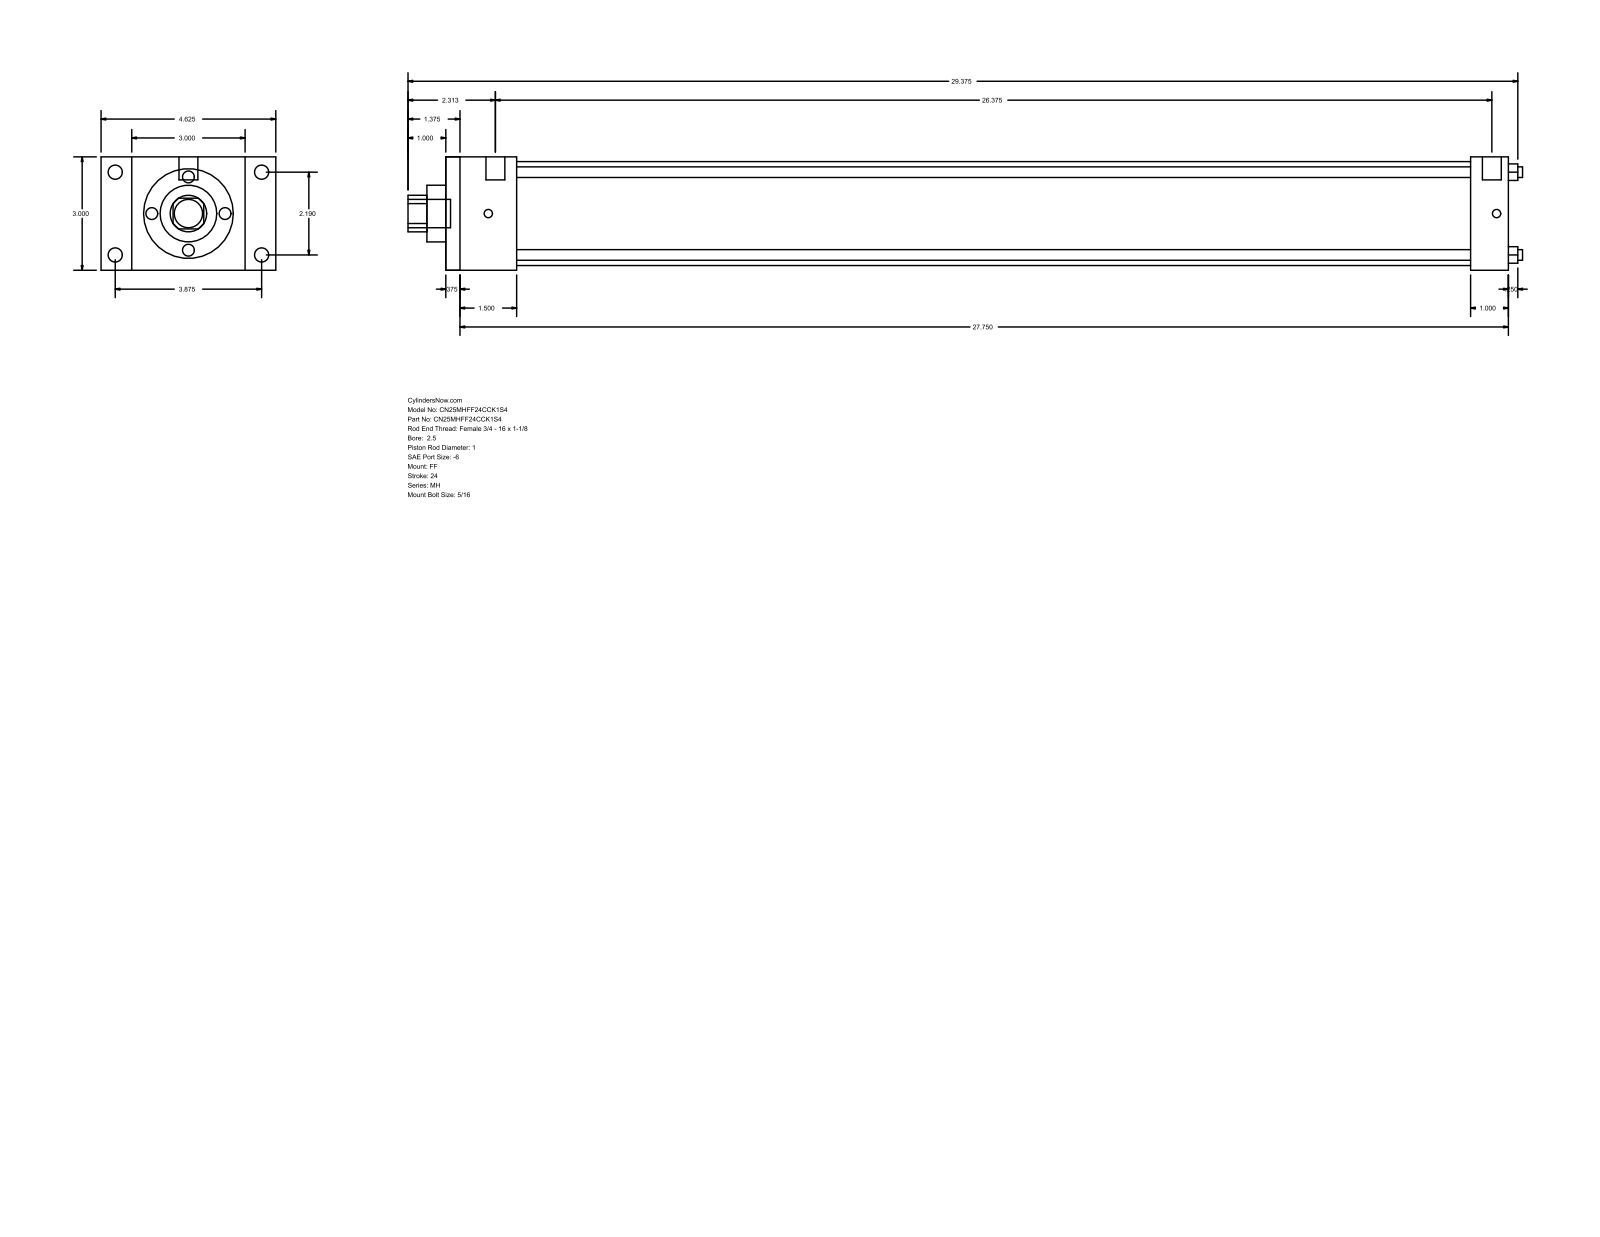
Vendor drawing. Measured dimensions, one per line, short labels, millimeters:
name: MH_FF__0250_1
written by: GSSL Pune (CONFIG_CONTROL_DESIGN)
unit: mm
bodies: 0 solids, 92 faces (64 planar, 28 cylindrical, 0 other)
size: 749.3 × 117.47 × 76.2
holes: 4× ⌀7.14, 1× ⌀25.4, 1× ⌀38.1, 1× ⌀69.85
bosses: 4× ⌀9.53, 4× ⌀5.56, 2× ⌀12.7, 1× ⌀19.05
rounds: 1× R12.29
face distances: 76.2, 714.37, 704.85, 9.52, 25.39, 47.63, 688.98, 38.11, 679.46, 641.35
hole spacings: 39.33, 55.62, 78.66
